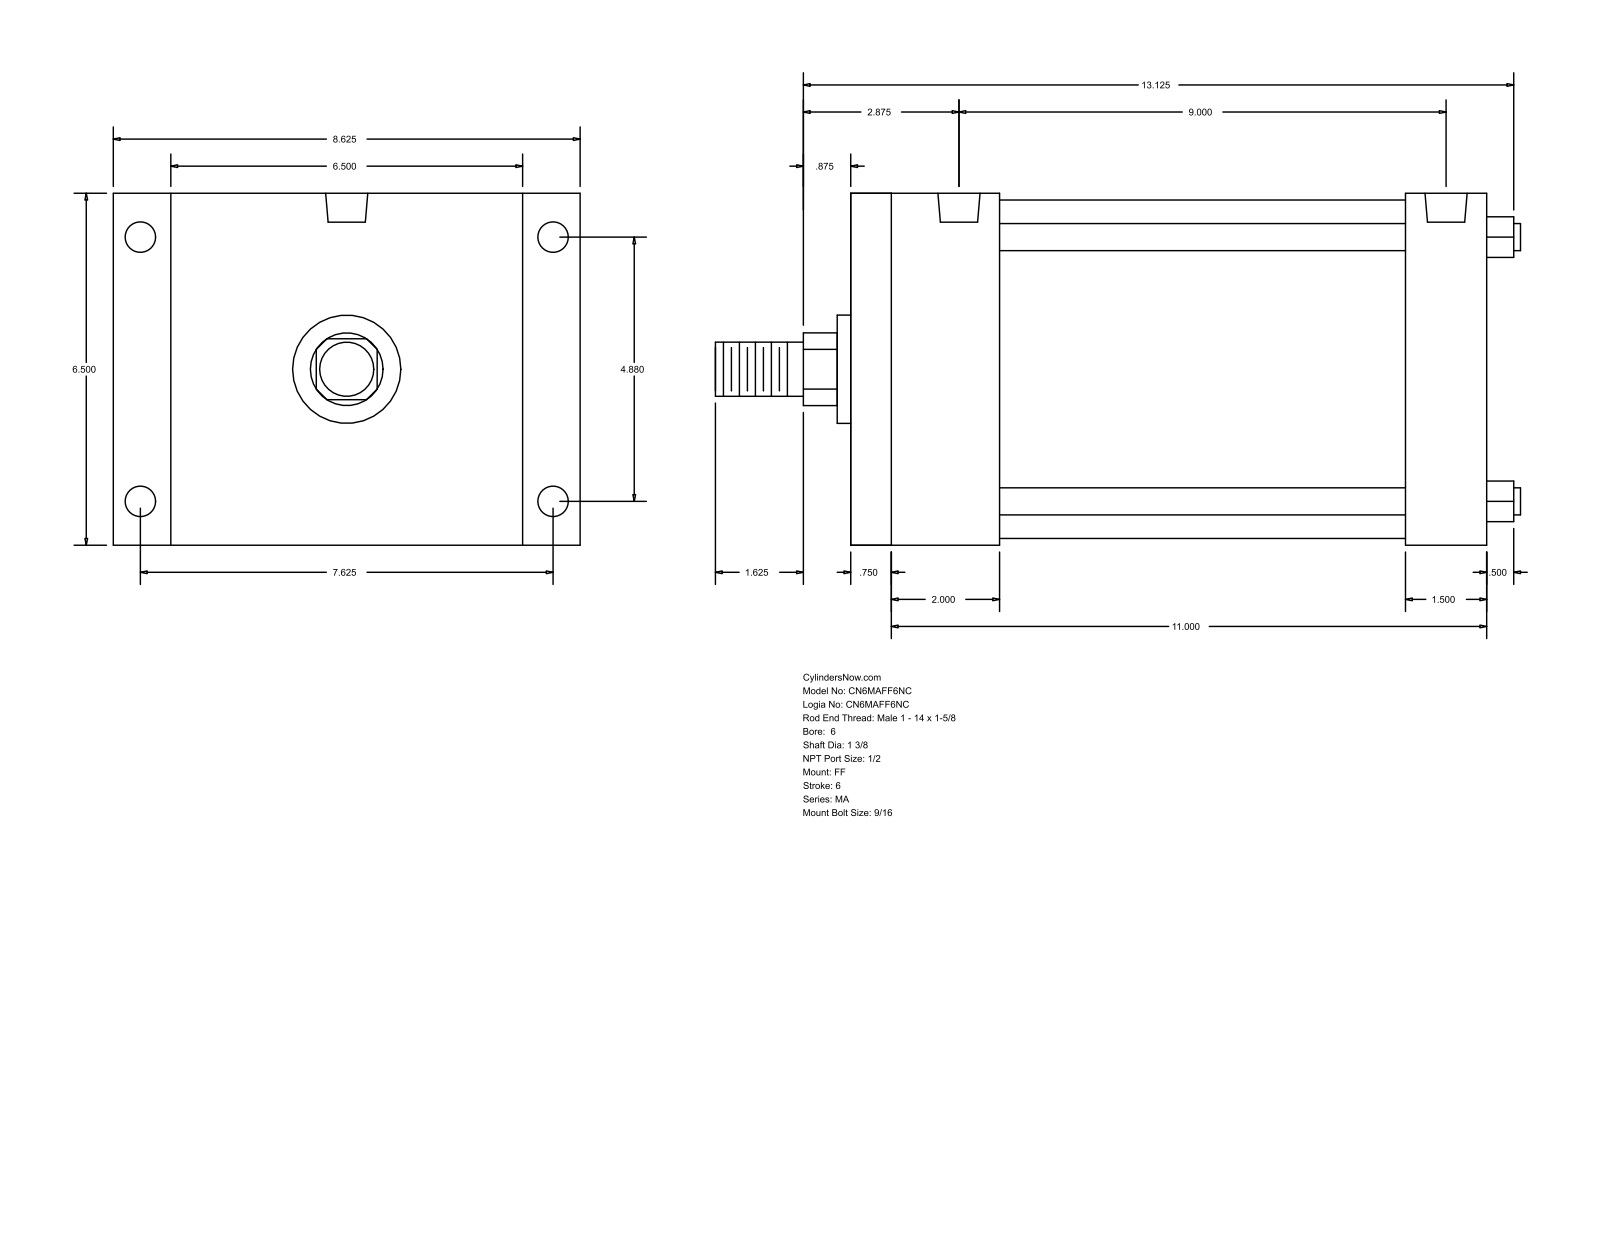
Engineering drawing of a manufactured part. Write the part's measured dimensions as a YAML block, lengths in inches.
part_name: "MA_FF__0600_1.375"
step_written_by: "GSSL Pune (CONFIG_CONTROL_DESIGN)"
units: inches
bodies: {solids: 0, faces: 92, planar: 64, cylindrical: 28, other: 0}
overall_size: [14.875, 8.625, 6.5]
round_holes:
  - {diameter: 0.563, count: 4}
  - {diameter: 0.687, count: 4}
  - {diameter: 0.778, count: 2}
round_bosses_or_shafts:
  - {diameter: 0.5, count: 4}
  - {diameter: 6.25, count: 1}
  - {diameter: 2, count: 1}
  - {diameter: 1.375, count: 1}
  - {diameter: 1, count: 1}
partial_cylinders:
  - {radius: 0.672, count: 1}
face_to_face_distances: [6.5, 11.75, 0.625, 11.125, 2.625, 2, 9.125, 10.25, 9.625, 7.625]
hole_center_spacings: [4.88, 7.625, 9.053, 9.125, 0.125, 9]
